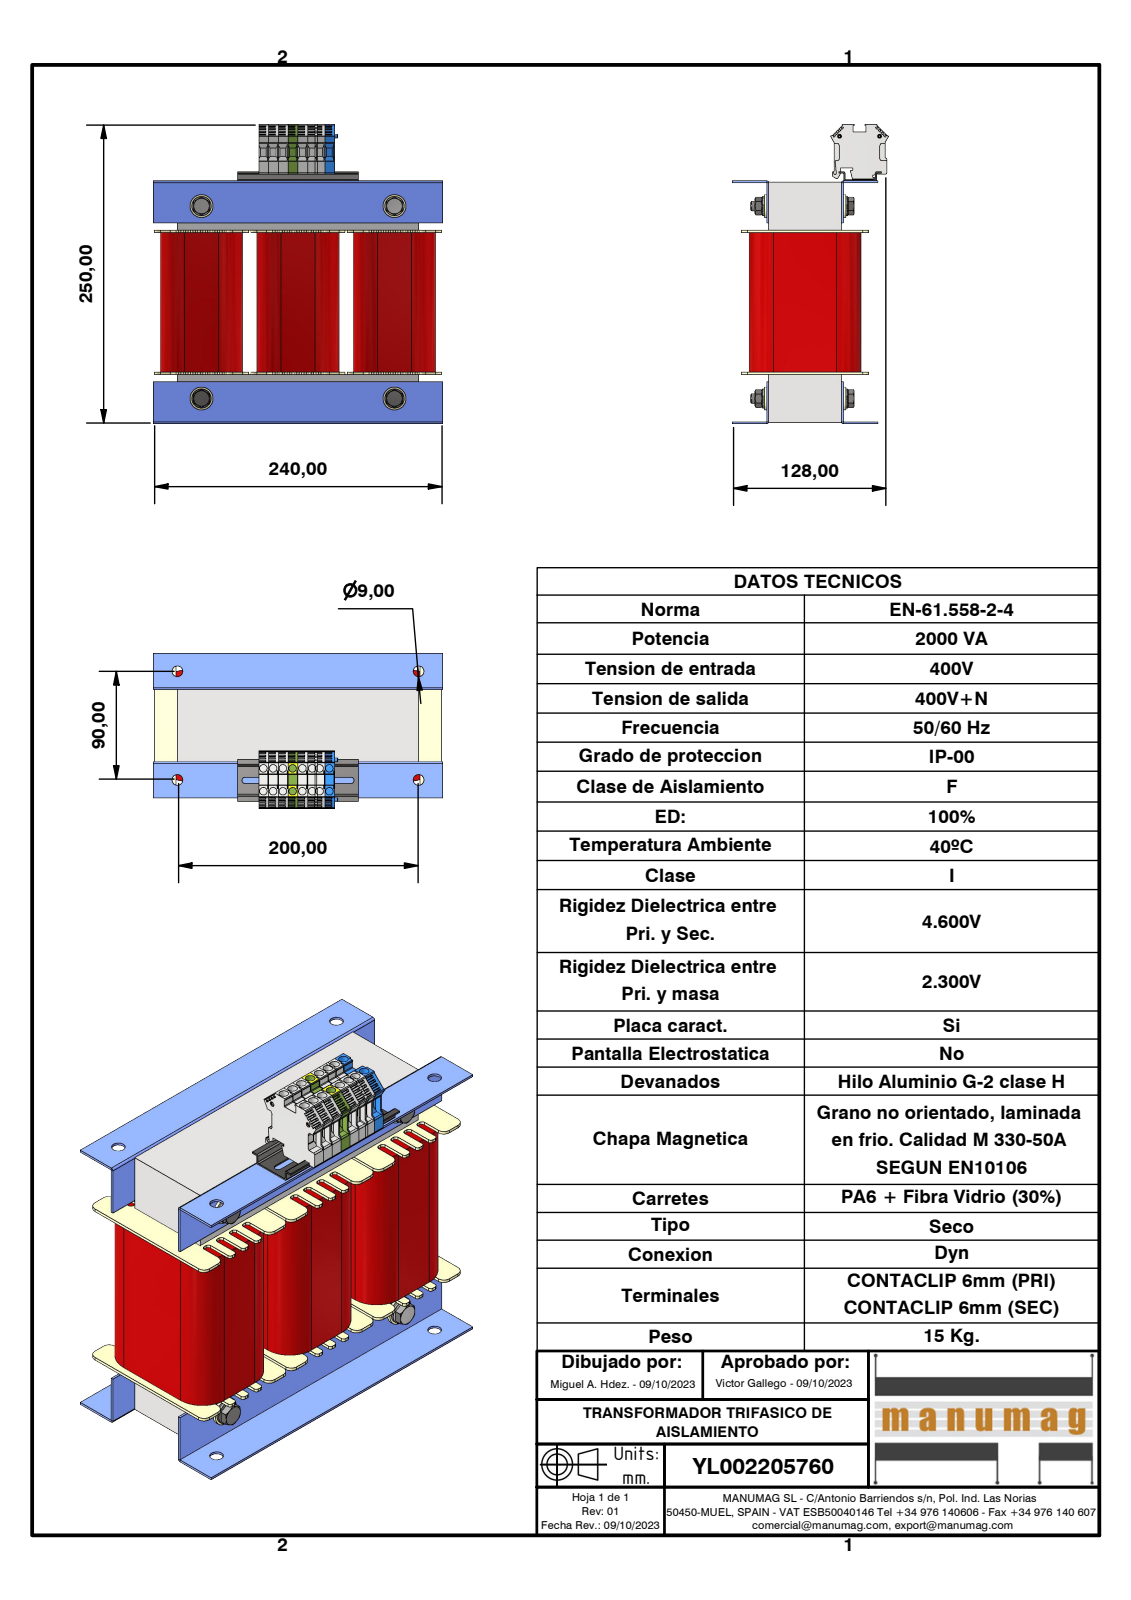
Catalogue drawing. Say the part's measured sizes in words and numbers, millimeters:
The part is named "YL002205760; 3UI120 200 x 200 - 60 (Rc40); UI 120_60; RC40 NT040 (+8 more)". Its 3-D file was written by "Autodesk Inventor 2023 (AUTOMOTIVE_DESIGN)". It is 41 solids with 2898 faces: 2018 planar, 712 cylindrical and 168 other. Overall it measures 249.05 by 240 by 128.9 millimeters. Its volume is 3 300 000 cubic millimeters and its surface area 582 876 square millimeters. Round holes: 16 of diameter 6.3, 4 of diameter 6.65, 4 of diameter 8, 4 of diameter 8.4, 4 of diameter 9, 4 of diameter 10.5, 4 of diameter 11, 2 of diameter 2.4, 2 of diameter 2.5, 2 of diameter 2.75, 2 of diameter 2.95. Round bosses or shafts: 4 of diameter 19, 4 of diameter 16, 4 of diameter 11.4, 4 of diameter 9.6, 4 of diameter 7.32. Partial cylindrical surfaces (rounded edges, fillets, slot ends): 85 of radius 2, 24 of radius 5, 16 of radius 0.25, 15 of radius 1, 12 of radius 20, 8 of radius 2.6, 5 of radius 0.3, 5 of radius 0.5. The main face-to-face distances are 40, 80, 160, 60, 120, 1.5, 14, 54, 61.5, 200. The hole center spacings are 8.1, 20.65, 16.2, 19, 24.97, 24.3, 30.85, 14.25.
